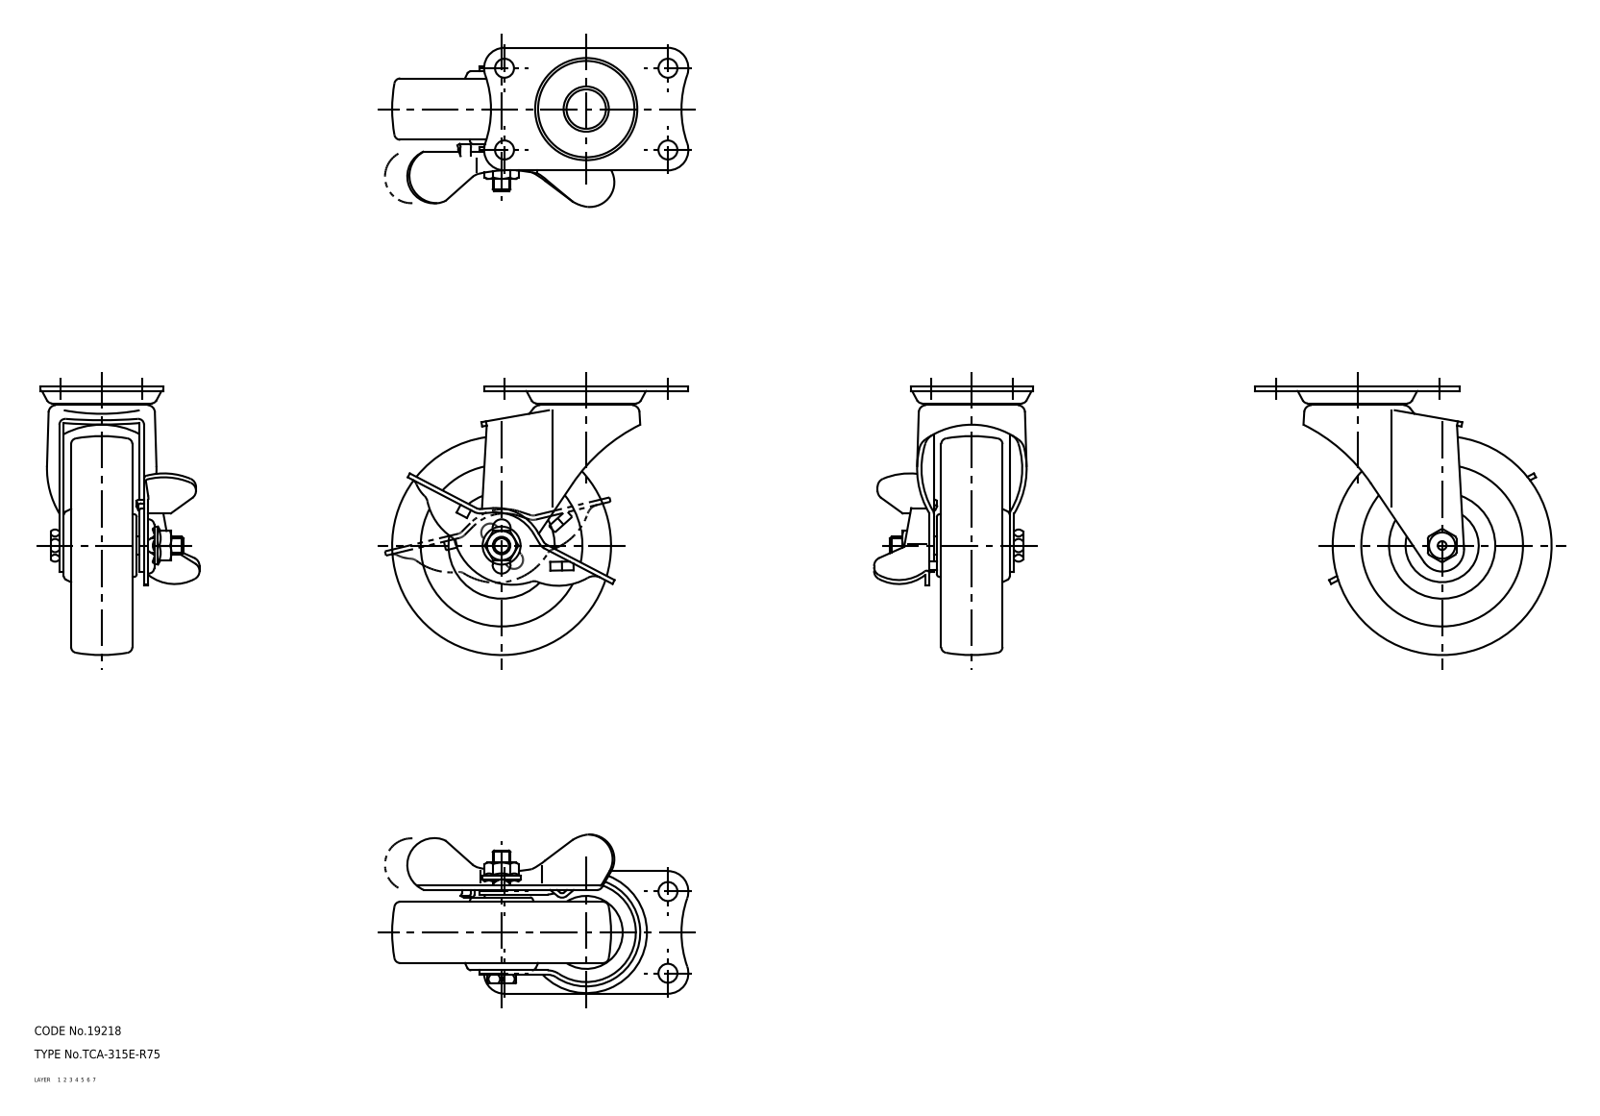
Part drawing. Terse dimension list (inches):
name: lever; wheel; mounting plate; main shaft (+2 more)
written by: CADfix (AUTOMOTIVE_DESIGN)
unit: in
bodies: 8 solids, 370 faces (0 planar, 0 cylindrical, 370 other)
size: 3.996 × 3.622 × 2.14
volume: 6.632 in³; area: 60.16 in²
